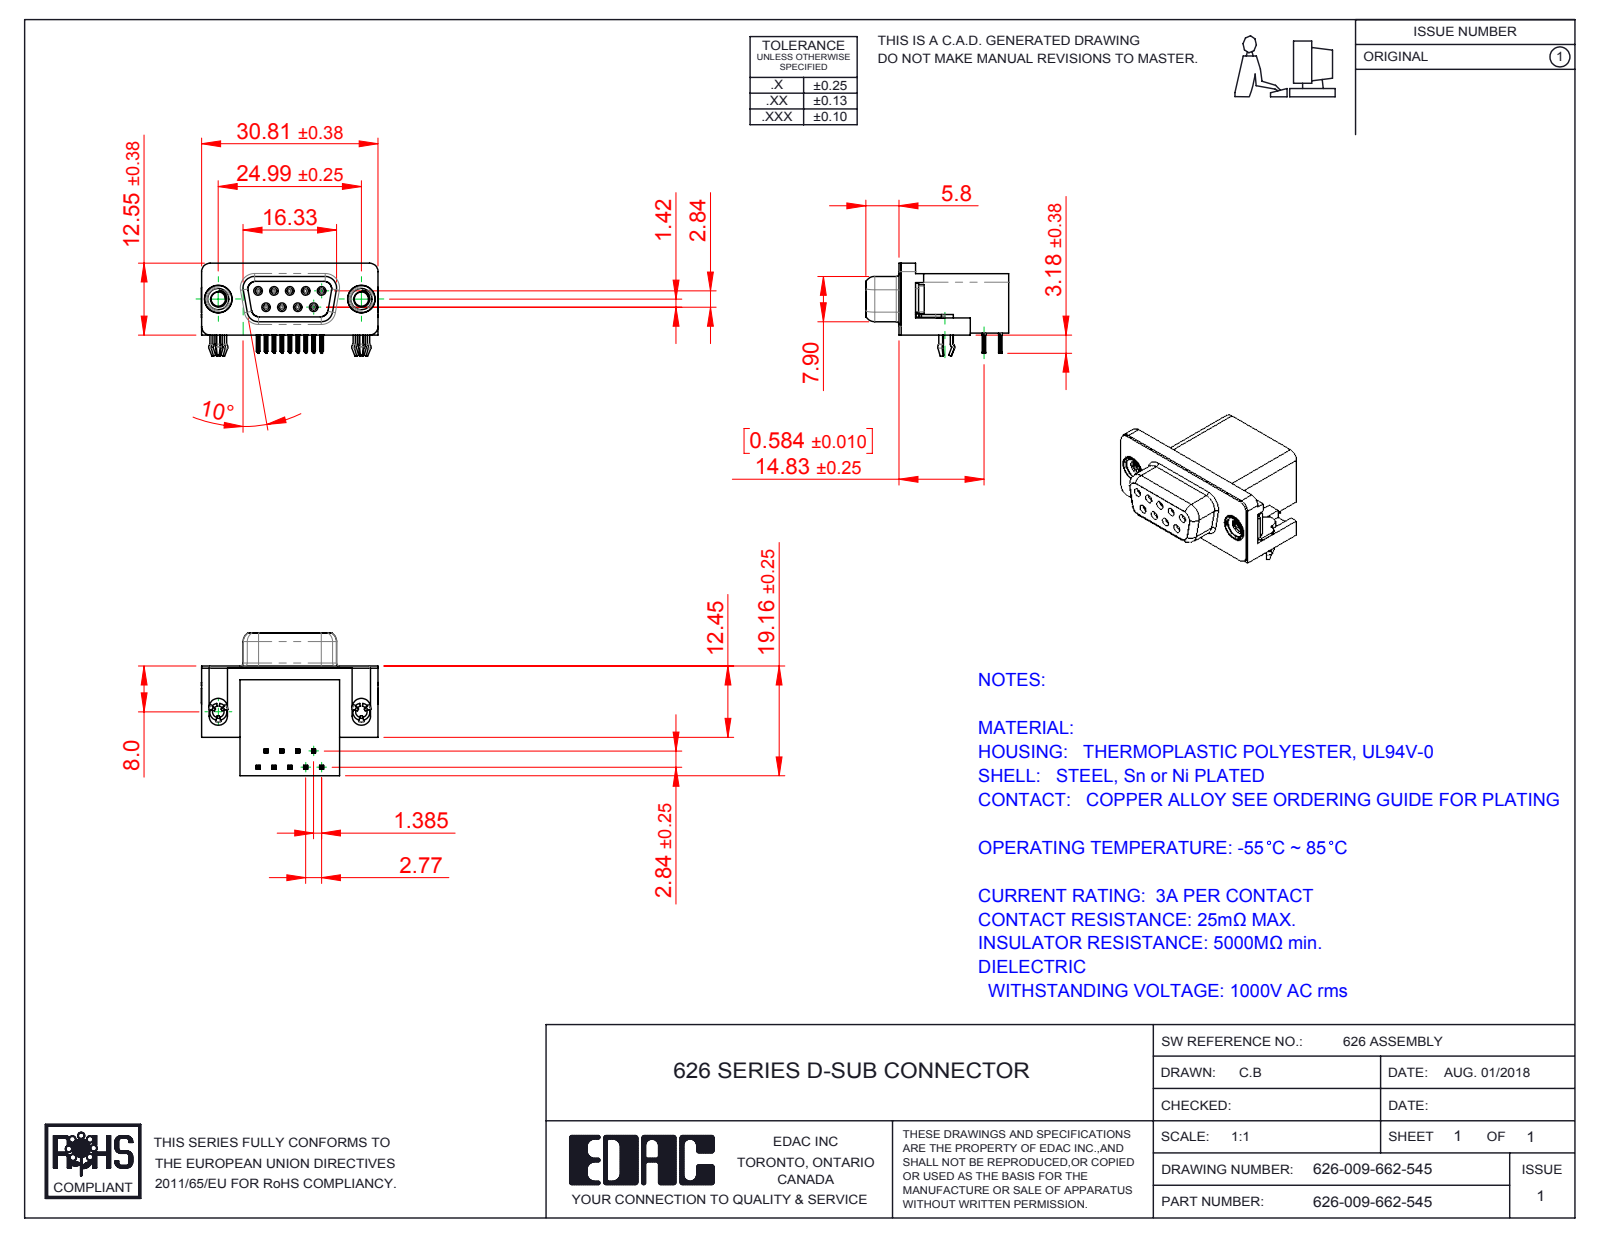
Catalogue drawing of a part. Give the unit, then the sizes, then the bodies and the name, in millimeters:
Units: millimetres
Overall size (bounding box): 30.89 × 24.96 × 16.25
Round holes (diameter × count): ⌀0.8 ×9, ⌀0.9 ×9, ⌀2 ×2, ⌀2.5 ×2, ⌀4 ×2, ⌀4.8 ×2, ⌀5 ×2
Round bosses / shafts (diameter × count): ⌀1.2 ×9, ⌀4.9 ×2, ⌀4.75 ×2, ⌀3.9 ×2, ⌀3 ×2
Partial cylindrical surfaces — rounded edges, fillets, slot ends (radius × count): R0.1 ×72, R0.15 ×36, R0.35 ×18, R1 ×18, R0.25 ×12, R0.34 ×9, R1.35 ×8, R1.6 ×8
Main face-to-face distances: 0.4, 10.34, 0.35, 18.76, 19.16, 2.9, 2.5, 6.2, 16.26, 10.69
Hole centre spacings: 3.16, 2.77, 5.54, 5.03, 5.04, 8.31, 7.48, 7.49
Volume: 4 972 mm³ · Surface area: 5 855 mm²
Bodies: 15 solids, 1676 faces (722 planar, 426 cylindrical, 528 other)
Part name (STEP PRODUCT): 626 Contact Bottom; 626-009-662-545; 626 Shell_9 Socket; 626 3 Prong Board Lock (+3 more)
STEP written by: SolidWorks 2016 (CONFIG_CONTROL_DESIGN)
